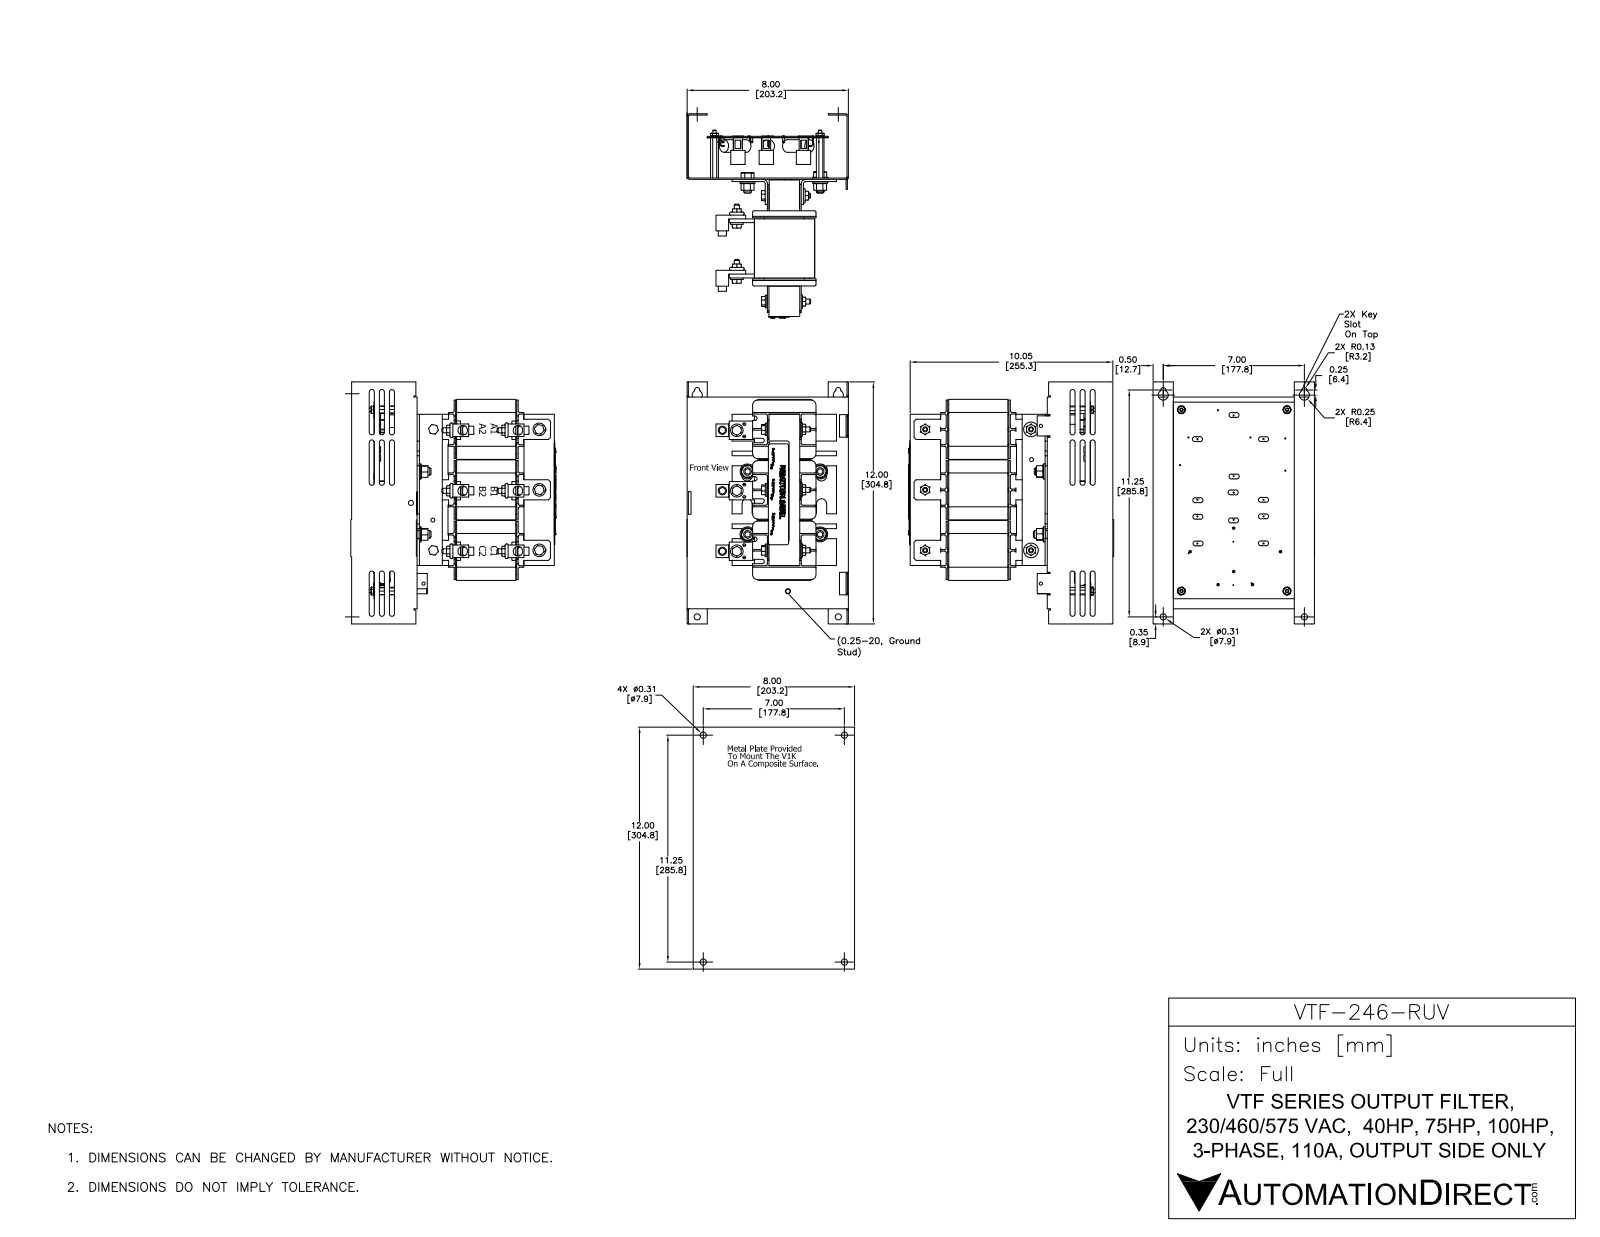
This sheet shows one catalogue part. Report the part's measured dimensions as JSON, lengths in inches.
{"part_name": "VTF 110A r1 from XT Coordfix", "step_written_by": "SolidWorks 2017 (AUTOMOTIVE_DESIGN)", "units": "inches", "bodies": {"solids": 80, "faces": 5186, "planar": 2433, "cylindrical": 1967, "other": 786}, "overall_size": [12, 10.171, 8.005], "volume_in3": 152.7, "surface_area_in2": 1477, "round_holes": [[0.06, 24], [0.25, 9], [0.31, 8], [0.38, 8], [0.138, 6], [0.281, 6], [0.476, 6], [0.164, 4], [0.22, 4], [0.307, 4], [0.262, 3], [0.266, 3]], "round_bosses_or_shafts": [[0.03, 12], [0.046, 11], [0.625, 9], [0.728, 8], [0.125, 6], [0.75, 4], [0.406, 3], [0.164, 3]], "partial_cylinders_radius": [[0.03, 168], [0.03, 128], [0.075, 117], [0.06, 78], [0.125, 78], [0.02, 60], [0.028, 60], [0.25, 42]], "face_to_face_distances": [0.063, 2.074, 2.01, 3, 1.5, 7.937, 2.063, 2, 0.076, 1.6], "hole_center_spacings": [3, 6, 4.5, 6.047, 0.48, 1.5, 1.5, 2.74]}
